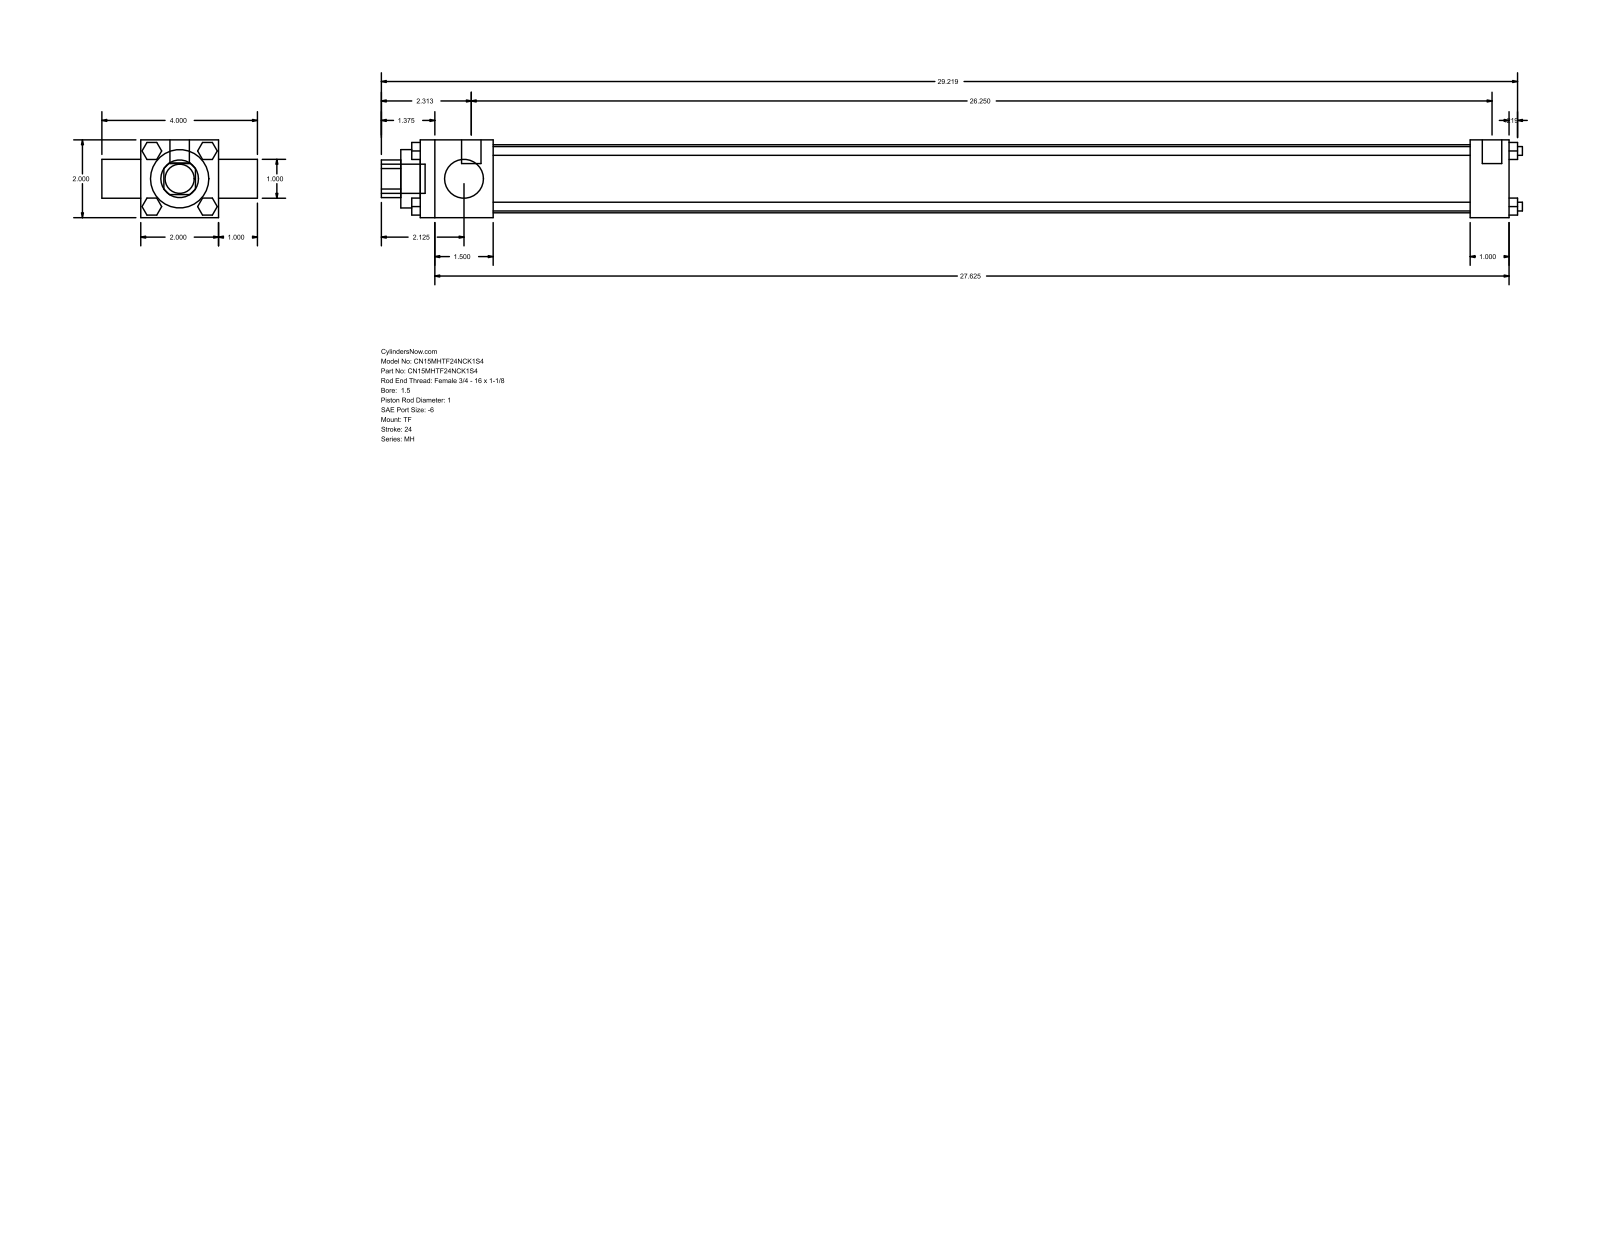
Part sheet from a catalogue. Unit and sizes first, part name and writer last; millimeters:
Units: millimetres
Overall size (bounding box): 745.33 × 101.6 × 50.8
Round holes (diameter × count): ⌀25.4 ×2, ⌀38.1 ×1, ⌀44.45 ×1
Round bosses / shafts (diameter × count): ⌀5.71 ×4, ⌀5.56 ×3, ⌀12.7 ×2, ⌀19.05 ×1
Partial cylindrical surfaces — rounded edges, fillets, slot ends (radius × count): R12.29 ×1
Main face-to-face distances: 50.8, 25.4, 711.2, 76.2, 47.63, 663.57, 685.8, 638.17, 716.76, 12.7
Bodies: 0 solids, 120 faces (92 planar, 28 cylindrical, 0 other)
Part name (STEP PRODUCT): MH_TF__0150_1
STEP written by: GSSL Pune (CONFIG_CONTROL_DESIGN)
